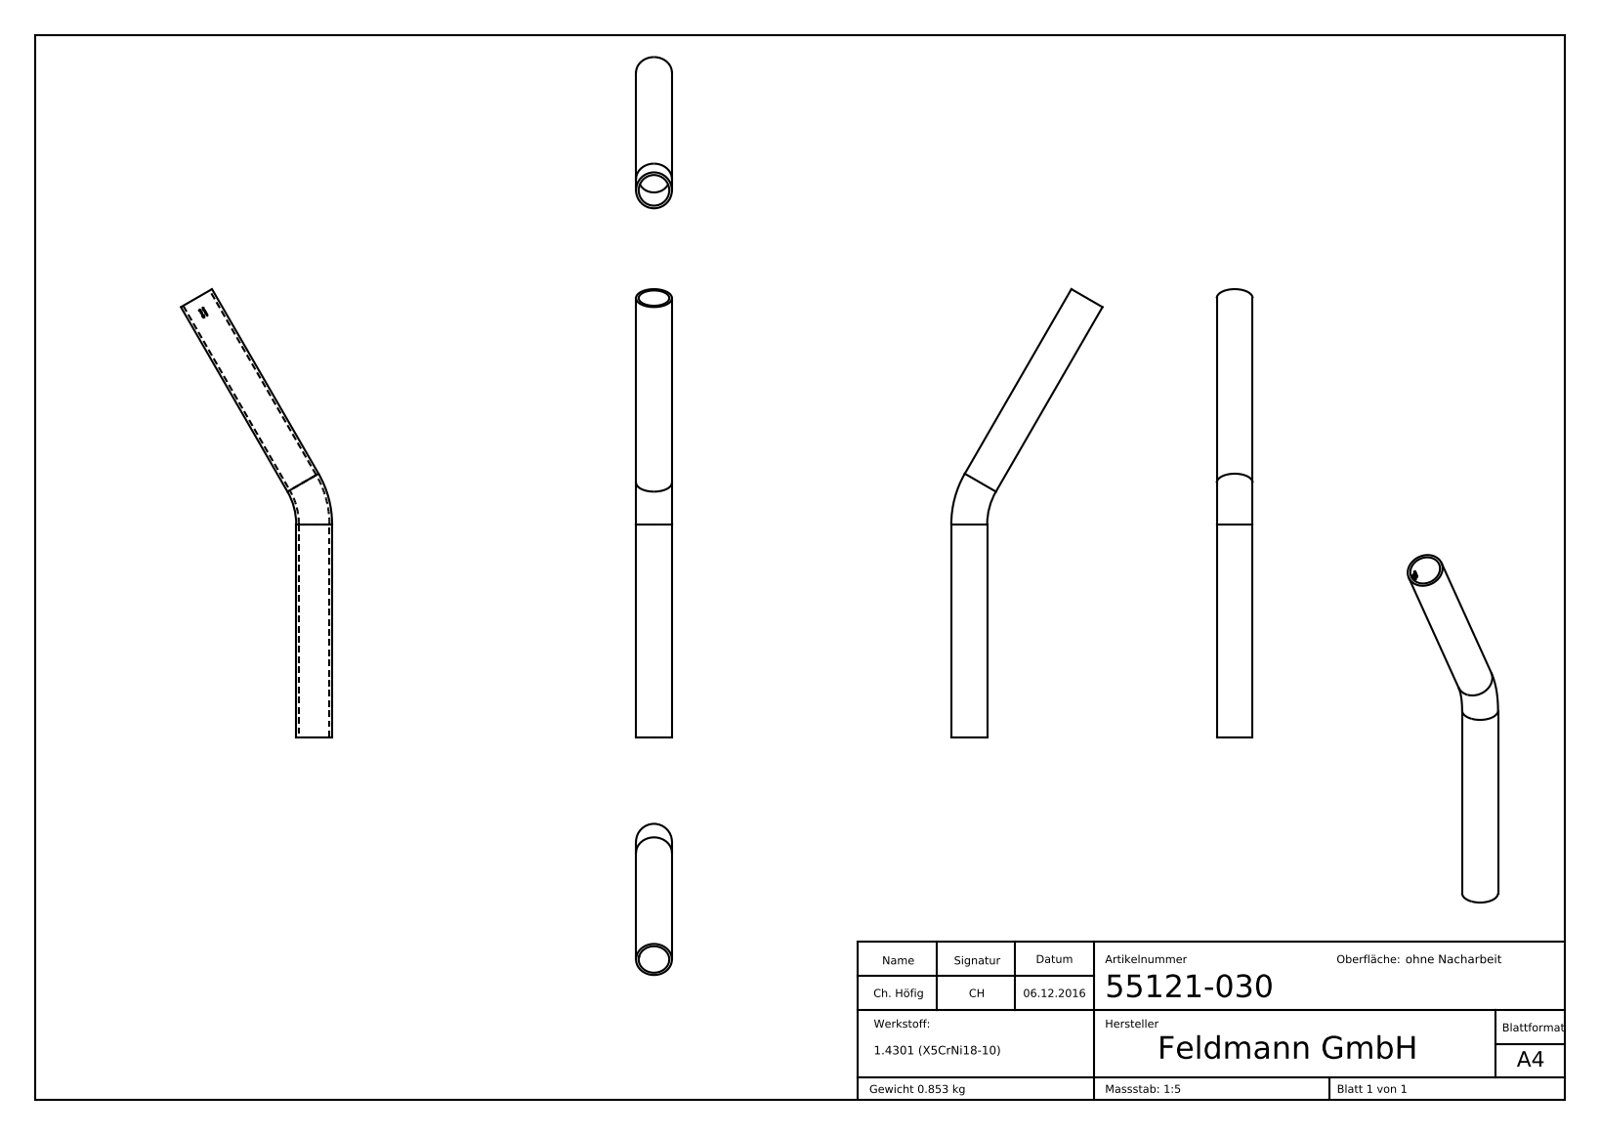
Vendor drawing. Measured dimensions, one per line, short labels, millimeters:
name: 55121-030
written by: SolidWorks 2015 (CONFIG_CONTROL_DESIGN)
unit: mm
bodies: 1 solid, 229 faces (93 planar, 30 cylindrical, 106 other)
size: 420.63 × 141.89 × 33.7
volume: 108 025 mm³; area: 86 920 mm²
holes: 2× ⌀28.7
bosses: 2× ⌀33.7
rounds: 1× R14.45
face distances: 2.97, 0.39, 2.43, 2.04, 4.49, 1.12, 1.91, 1.33, 4.23, 4.21
